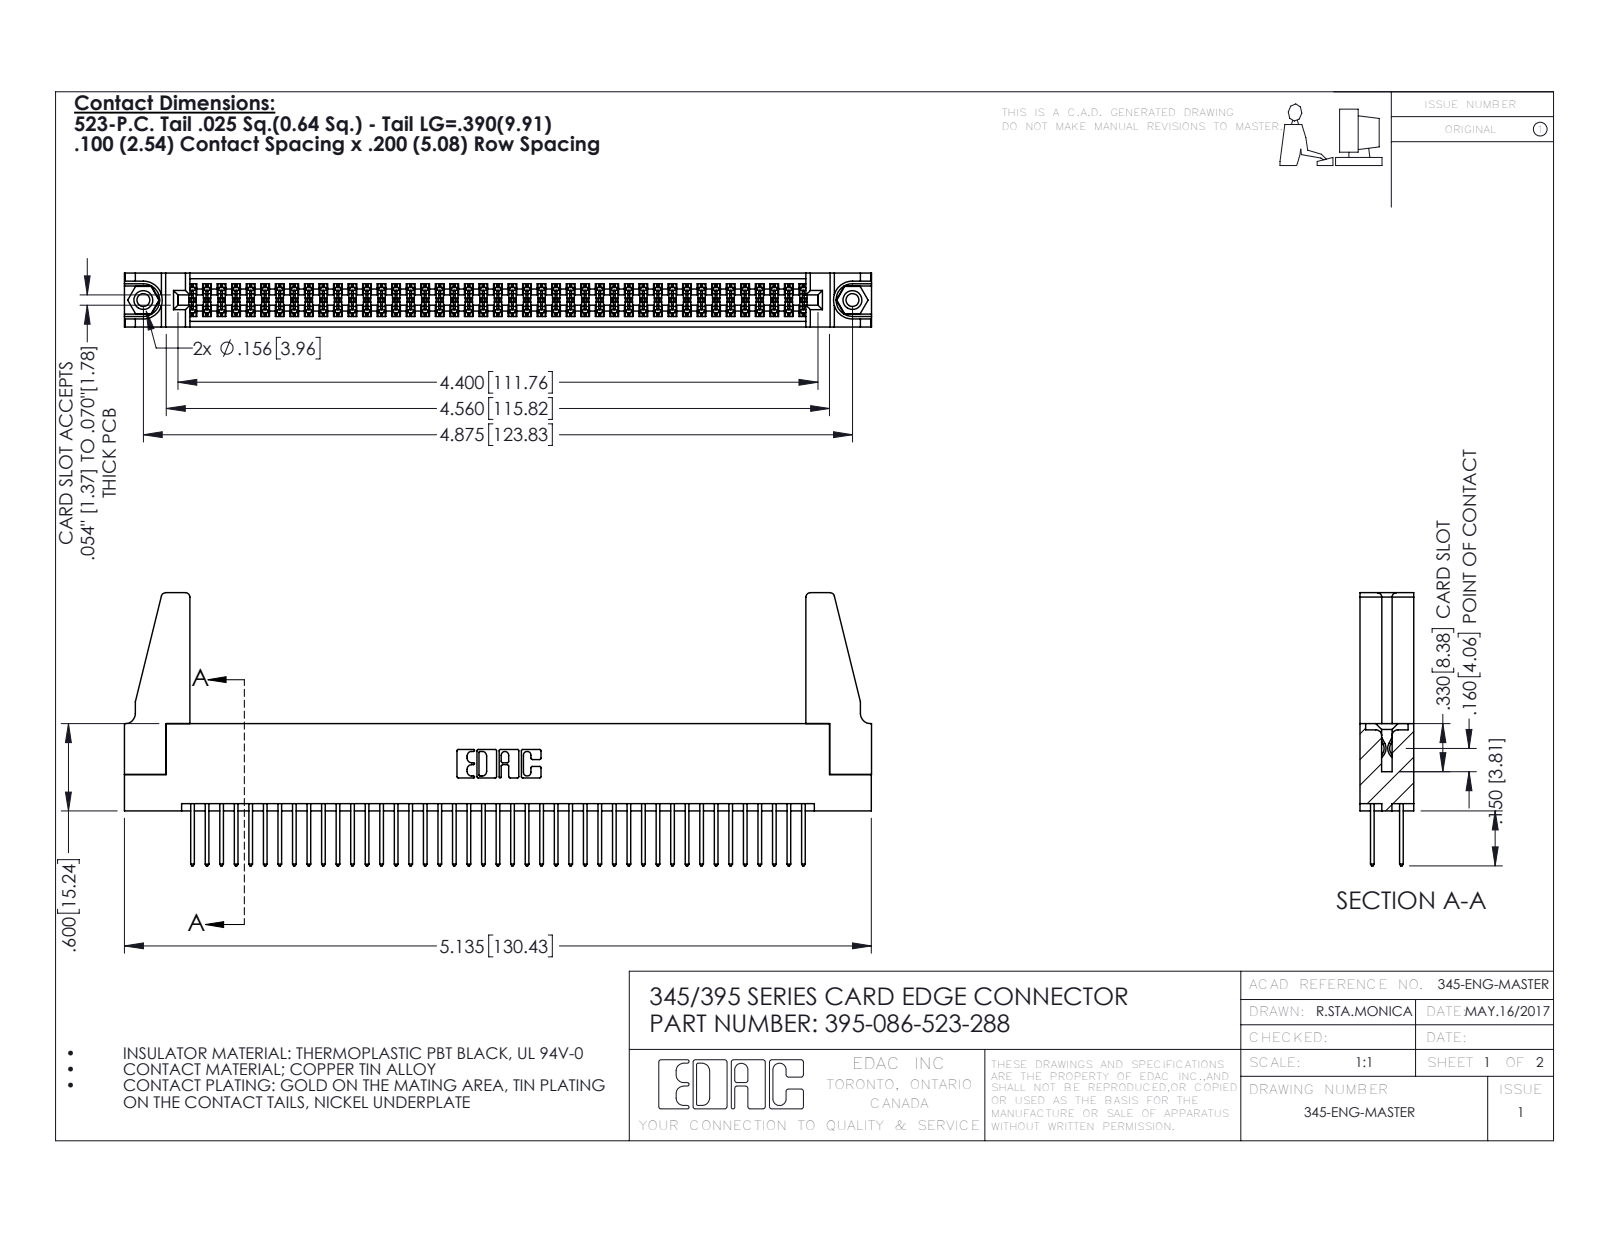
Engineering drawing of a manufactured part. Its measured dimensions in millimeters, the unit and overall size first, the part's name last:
Units: millimetres
Overall size (bounding box): 130.5 × 47.7 × 9.4
Round holes (diameter × count): ⌀2.3 ×2, ⌀3.2 ×2, ⌀4 ×2, ⌀1.6 ×1
Round bosses / shafts (diameter × count): ⌀3.9 ×2
Partial cylindrical surfaces — rounded edges, fillets, slot ends (radius × count): R0.2 ×129, R0.3 ×86, R0.3 ×22, R0.8 ×8, R0.2 ×6, R0.8 ×6, R0.7 ×3, R0.4 ×2
Main face-to-face distances: 1.8, 7.6, 5.1, 9.4, 2.5, 6.9, 0.6, 5.7, 4.4, 3.8
Hole centre spacings: 6.9, 117.8, 123.8
Volume: 16 100 mm³ · Surface area: 22 940 mm²
Bodies: 91 solids, 4550 faces (2990 planar, 1544 cylindrical, 16 other)
Part name (STEP PRODUCT): 345-292-001_345-293-123; 345-250-001_345-250-001-102; 345 Part_Flush Mounting Lugs - 0.156 Dia-TH; 395-086-523-288 (+1 more)
STEP written by: SolidWorks 2016 (CONFIG_CONTROL_DESIGN)
